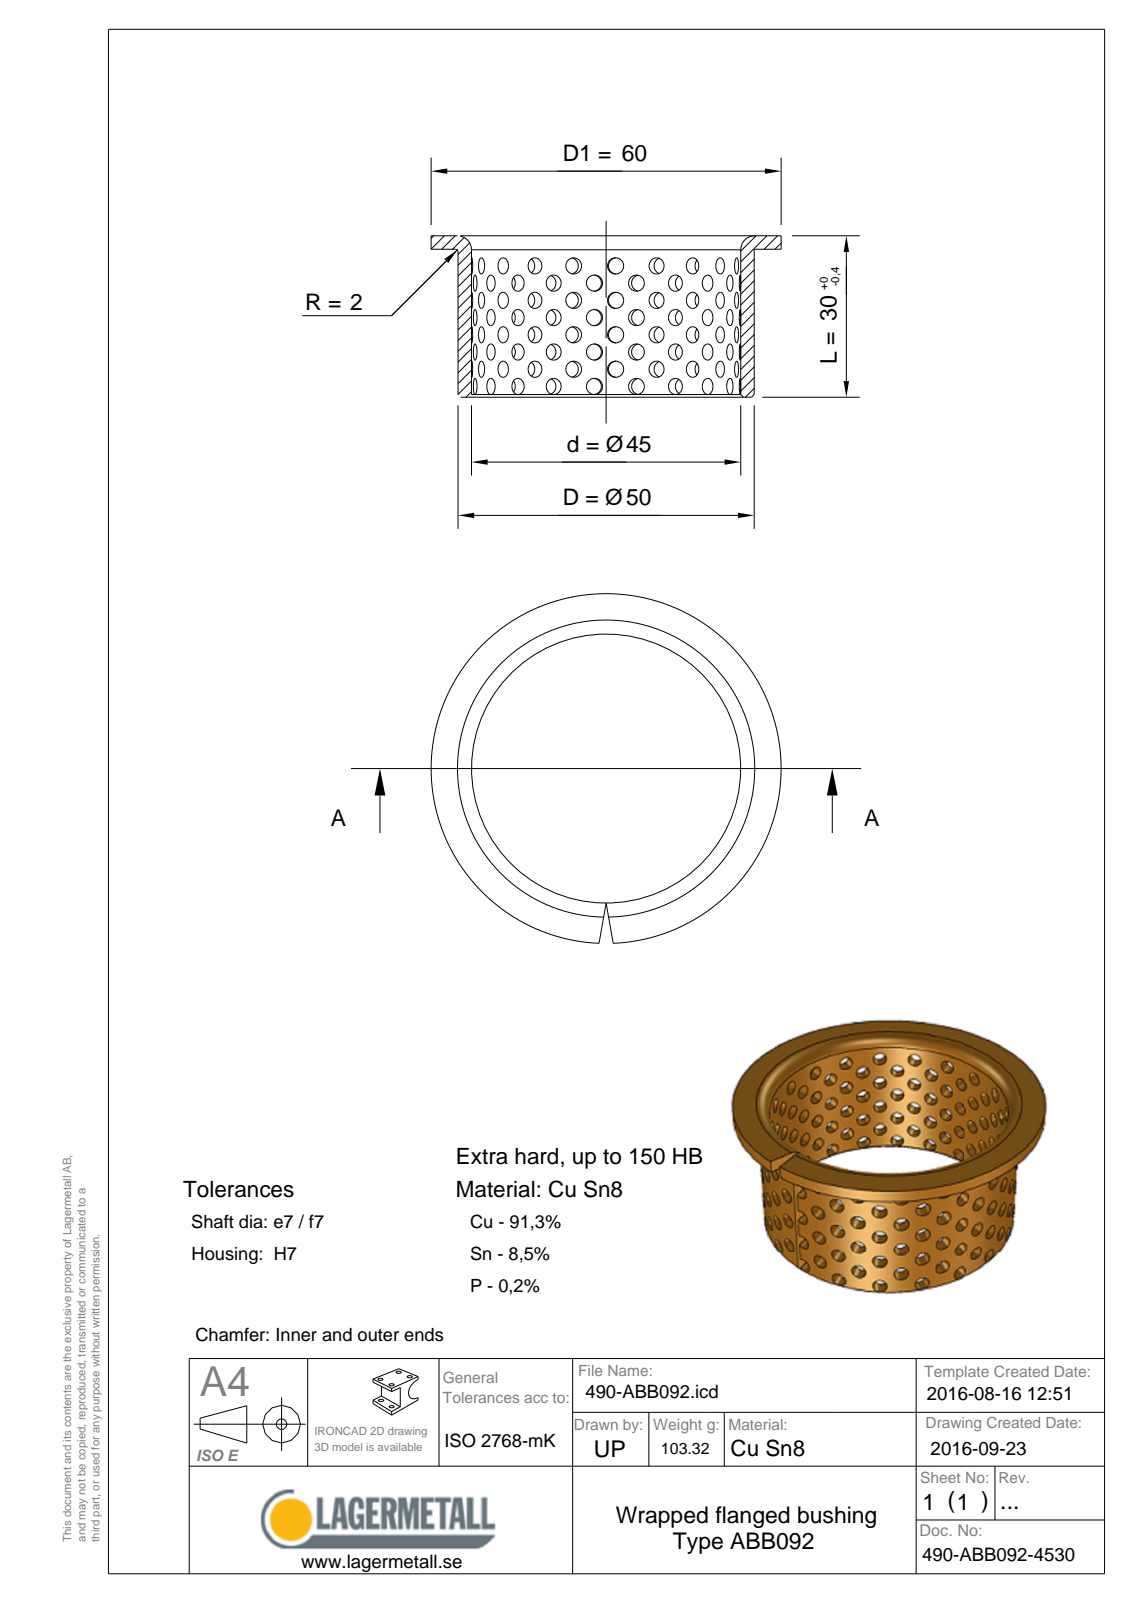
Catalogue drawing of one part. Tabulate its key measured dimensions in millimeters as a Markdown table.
| quantity | value |
| --- | --- |
| STEP written by | Spatial InterOp 3D (CONFIG_CONTROL_DESIGN) |
| units | millimeters |
| bodies | 1 solid, 25 faces (5 planar, 8 cylindrical, 12 other) |
| overall size | 60 × 60 × 30 |
| volume | 12 756 mm³ |
| surface area | 11 141 mm² |
| round holes (diameter × count) | 45 × 1 |
| round bosses / shafts (diameter × count) | 60 × 1, 50 × 1 |
| main face-to-face distances | 2.5, 27.5, 30 |
